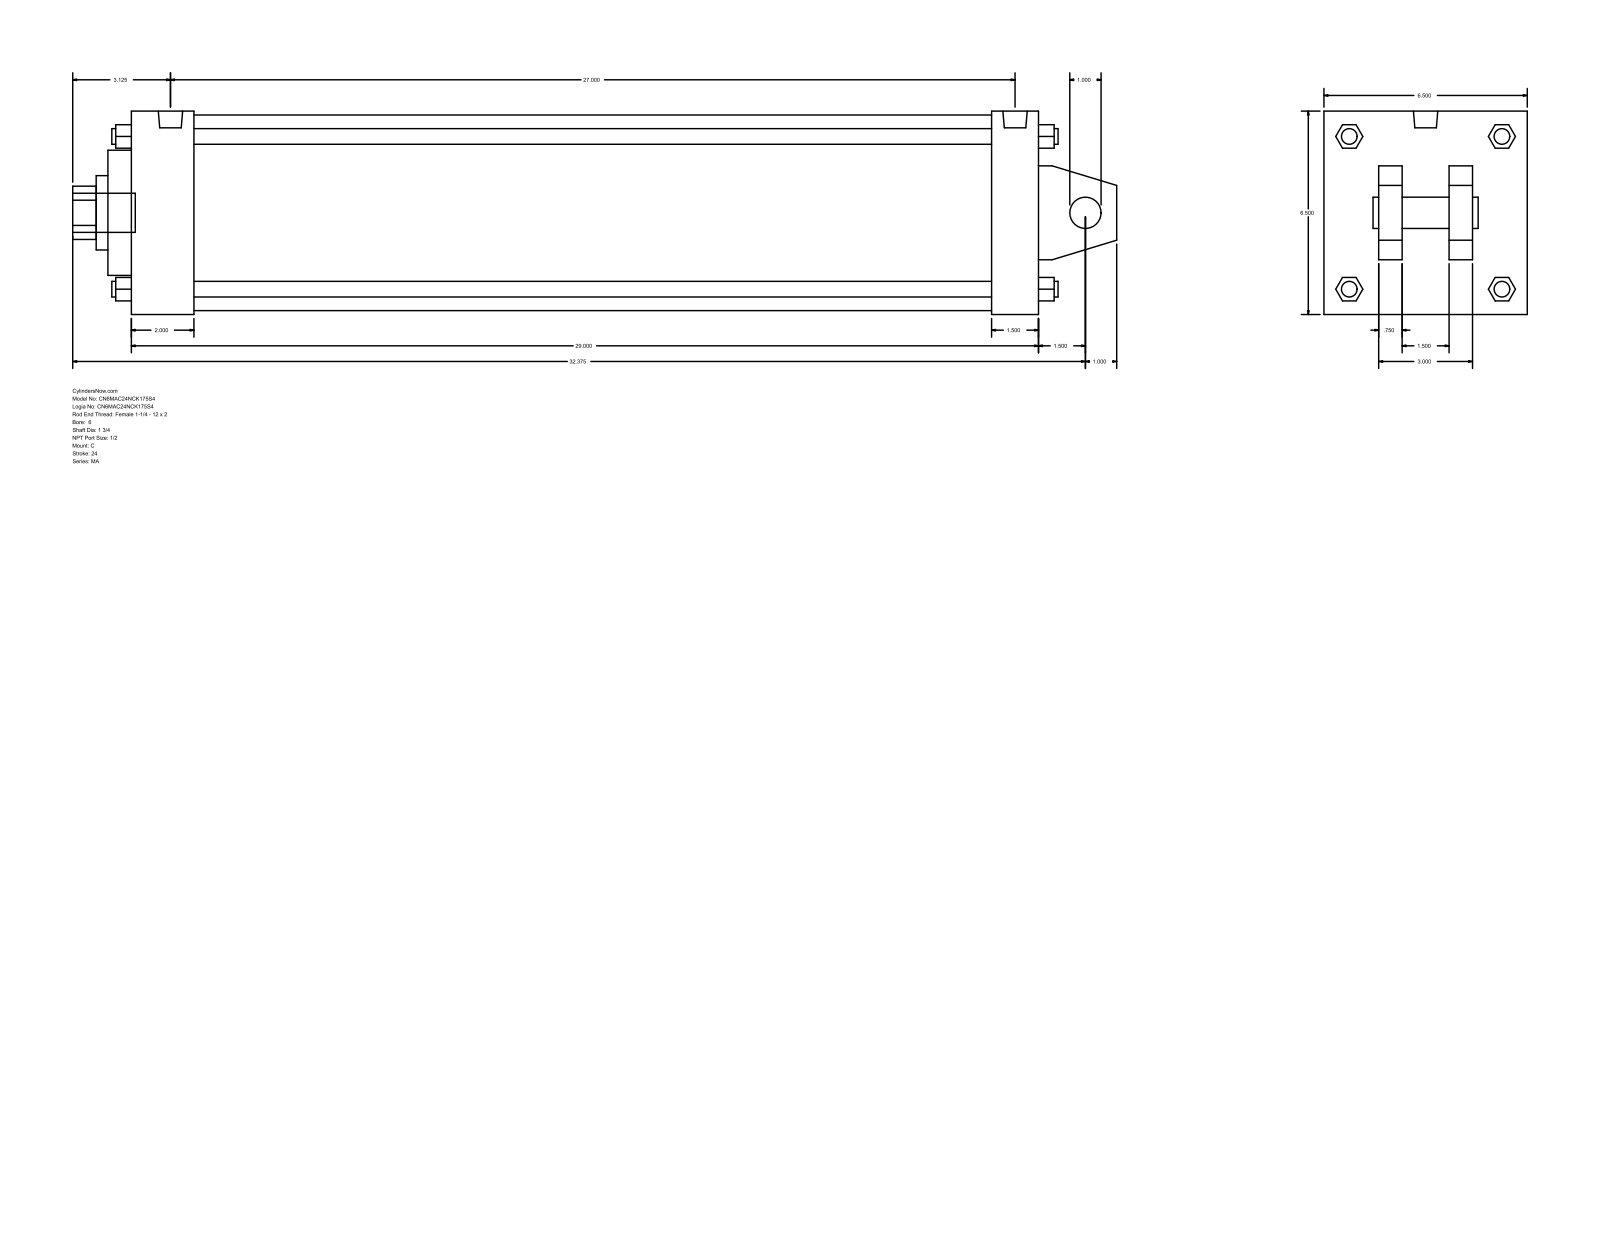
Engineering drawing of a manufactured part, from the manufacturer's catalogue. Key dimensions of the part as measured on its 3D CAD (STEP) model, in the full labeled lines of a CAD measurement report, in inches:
Part name (STEP PRODUCT): MA_C__0600_1.75
STEP written by: GSSL Pune (CONFIG_CONTROL_DESIGN)
Units: inches
Bodies: 0 solids, 141 faces (109 planar, 32 cylindrical, 0 other)
Overall size (bounding box): 33.375 × 6.5 × 6.5
Round holes (diameter × count): ⌀1 ×1, ⌀1.75 ×1, ⌀2.375 ×1, ⌀4 ×1, ⌀6.25 ×1
Round bosses / shafts (diameter × count): ⌀0.687 ×4, ⌀0.5 ×4, ⌀0.778 ×2, ⌀1.25 ×1
Partial cylindrical surfaces — rounded edges, fillets, slot ends (radius × count): R0.852 ×1
Main face-to-face distances: 6.5, 29, 0.75, 2.5, 4, 2, 1.75, 4.75, 27.5, 2.25
